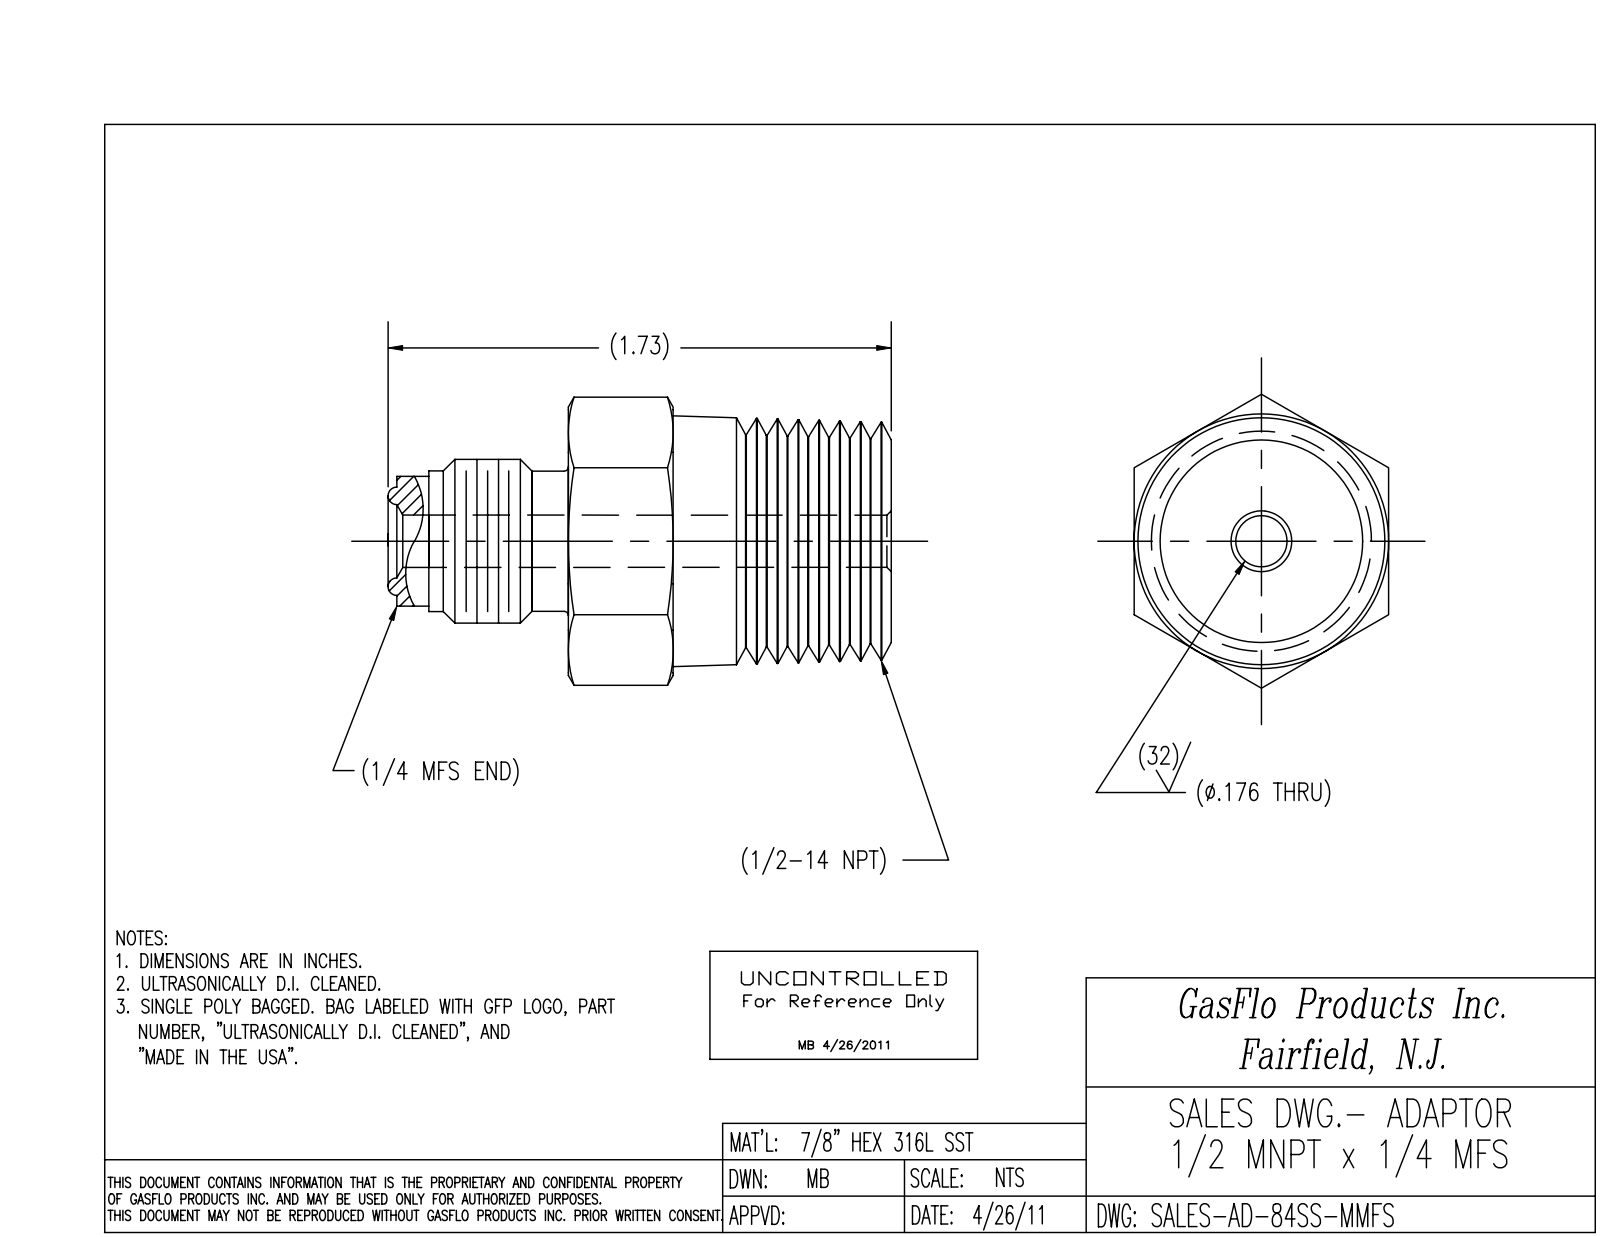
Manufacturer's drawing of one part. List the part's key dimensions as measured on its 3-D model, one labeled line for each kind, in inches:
Part name (STEP PRODUCT): AD-84SS-MMFS
STEP written by: SolidWorks 2018 (CONFIG_CONTROL_DESIGN)
Units: inches
Bodies: 1 solid, 95 faces (12 planar, 23 cylindrical, 60 other)
Overall size (bounding box): 1.73 × 1.01 × 0.875
Volume: 0.652 in³ · Surface area: 7.404 in²
Round holes (diameter × count): ⌀0.176 ×1, ⌀0.231 ×1
Round bosses / shafts (diameter × count): ⌀0.84 ×1, ⌀0.557 ×1, ⌀0.481 ×1, ⌀0.444 ×1, ⌀0.393 ×1
Main face-to-face distances: 1.11, 0.875, 0.21, 0.9, 0.62, 0.83, 1.73, 0.033, 0.587, 0.797
